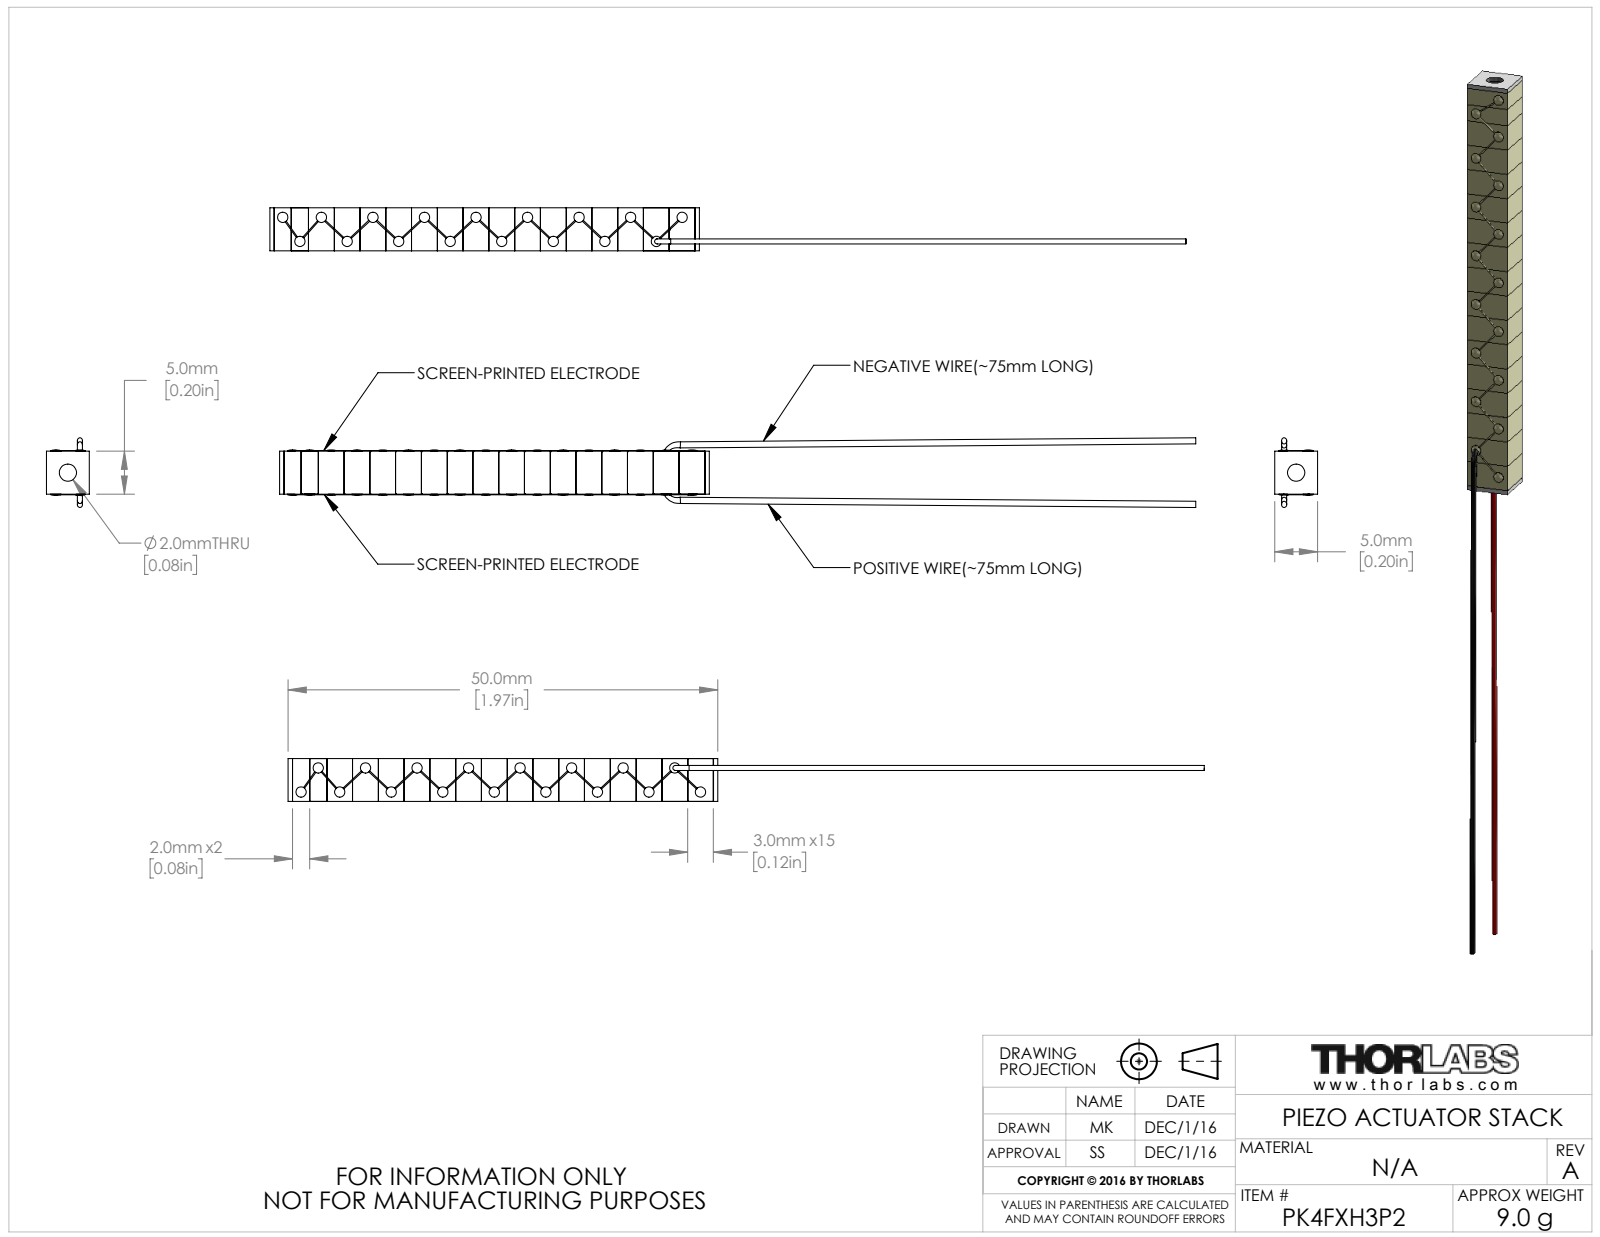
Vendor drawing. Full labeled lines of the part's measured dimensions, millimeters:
Part name (STEP PRODUCT): CTN009440
STEP written by: SolidWorks 2016 (AUTOMOTIVE_DESIGN)
Units: millimetres
Bodies: 48 solids, 434 faces (178 planar, 180 cylindrical, 76 other)
Overall size (bounding box): 106.66 × 8.12 × 5
Volume: 1 315 mm³ · Surface area: 2 876 mm²
Round holes (diameter × count): ⌀2 ×1
Round bosses / shafts (diameter × count): ⌀1.2 ×17
Main face-to-face distances: 3, 5, 6, 9, 12, 15, 18, 21, 24, 27
